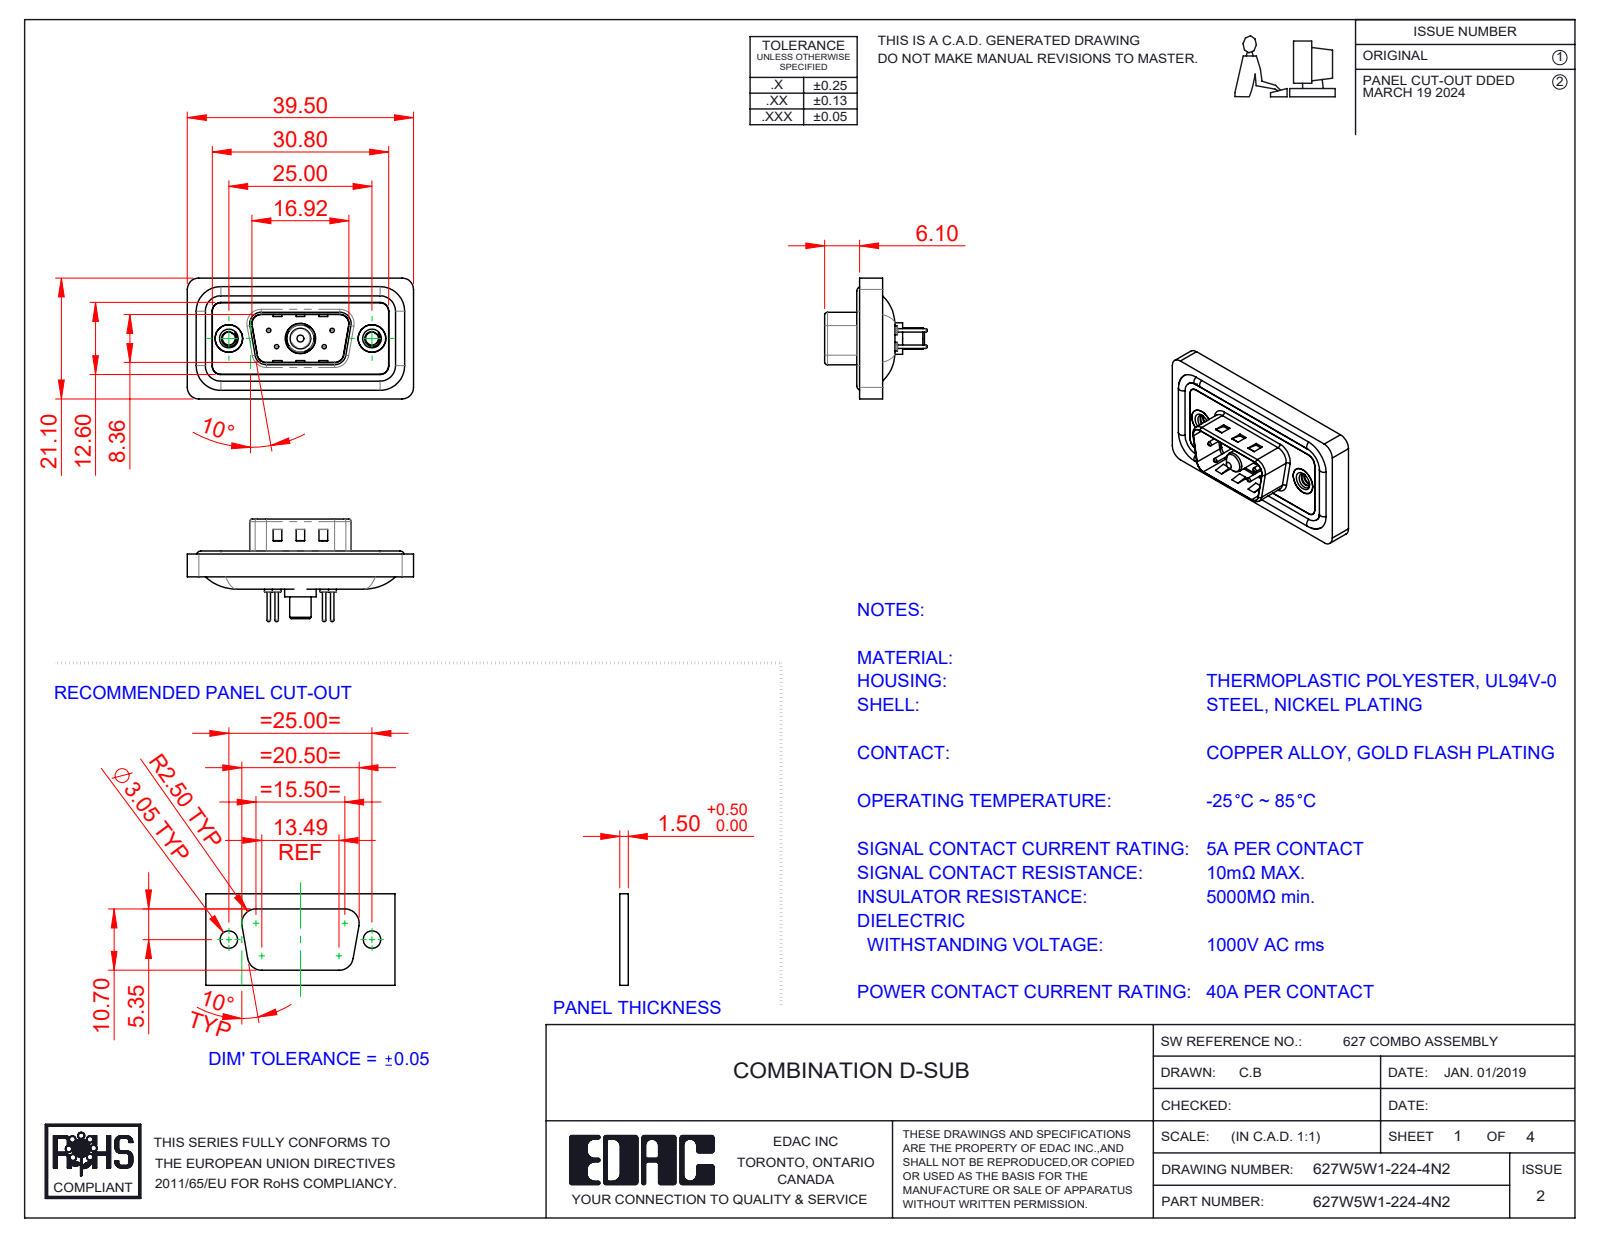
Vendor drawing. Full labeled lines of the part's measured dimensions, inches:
Part name (STEP PRODUCT): 627Combo Housing_5W1; 627Combo Shell Rear_09 Contacts; 627W5W1-224-4N2; 627Combo Contact Row 1_24 (+5 more)
STEP written by: SolidWorks 2023 (CONFIG_CONTROL_DESIGN)
Units: inches
Bodies: 13 solids, 598 faces (183 planar, 255 cylindrical, 160 other)
Overall size (bounding box): 1.555 × 0.831 × 0.705
Volume: 0.269 in³ · Surface area: 10.78 in²
Round holes (diameter × count): ⌀0.03 ×4, ⌀0.063 ×4, ⌀0.079 ×4, ⌀0.089 ×2, ⌀0.157 ×2, ⌀0.189 ×2, ⌀0.197 ×2, ⌀0.191 ×1, ⌀0.209 ×1
Round bosses / shafts (diameter × count): ⌀0.063 ×4, ⌀0.059 ×4, ⌀0.024 ×4, ⌀0.193 ×2, ⌀0.217 ×1, ⌀0.205 ×1, ⌀0.187 ×1, ⌀0.148 ×1
Partial cylindrical surfaces — rounded edges, fillets, slot ends (radius × count): R0.059 ×22, R0.079 ×18, R0.02 ×8, R0.063 ×8, R0.01 ×4, R0.024 ×4, R0.026 ×4, R0.035 ×4
Main face-to-face distances: 0.016, 0.043, 0.114, 0.063, 0.122, 0.02, 0.059, 0.098, 0.157, 0.031
Hole centre spacings: 0.124, 0.225, 0.28, 0.492, 0.713, 0.173, 0.173, 0.327
